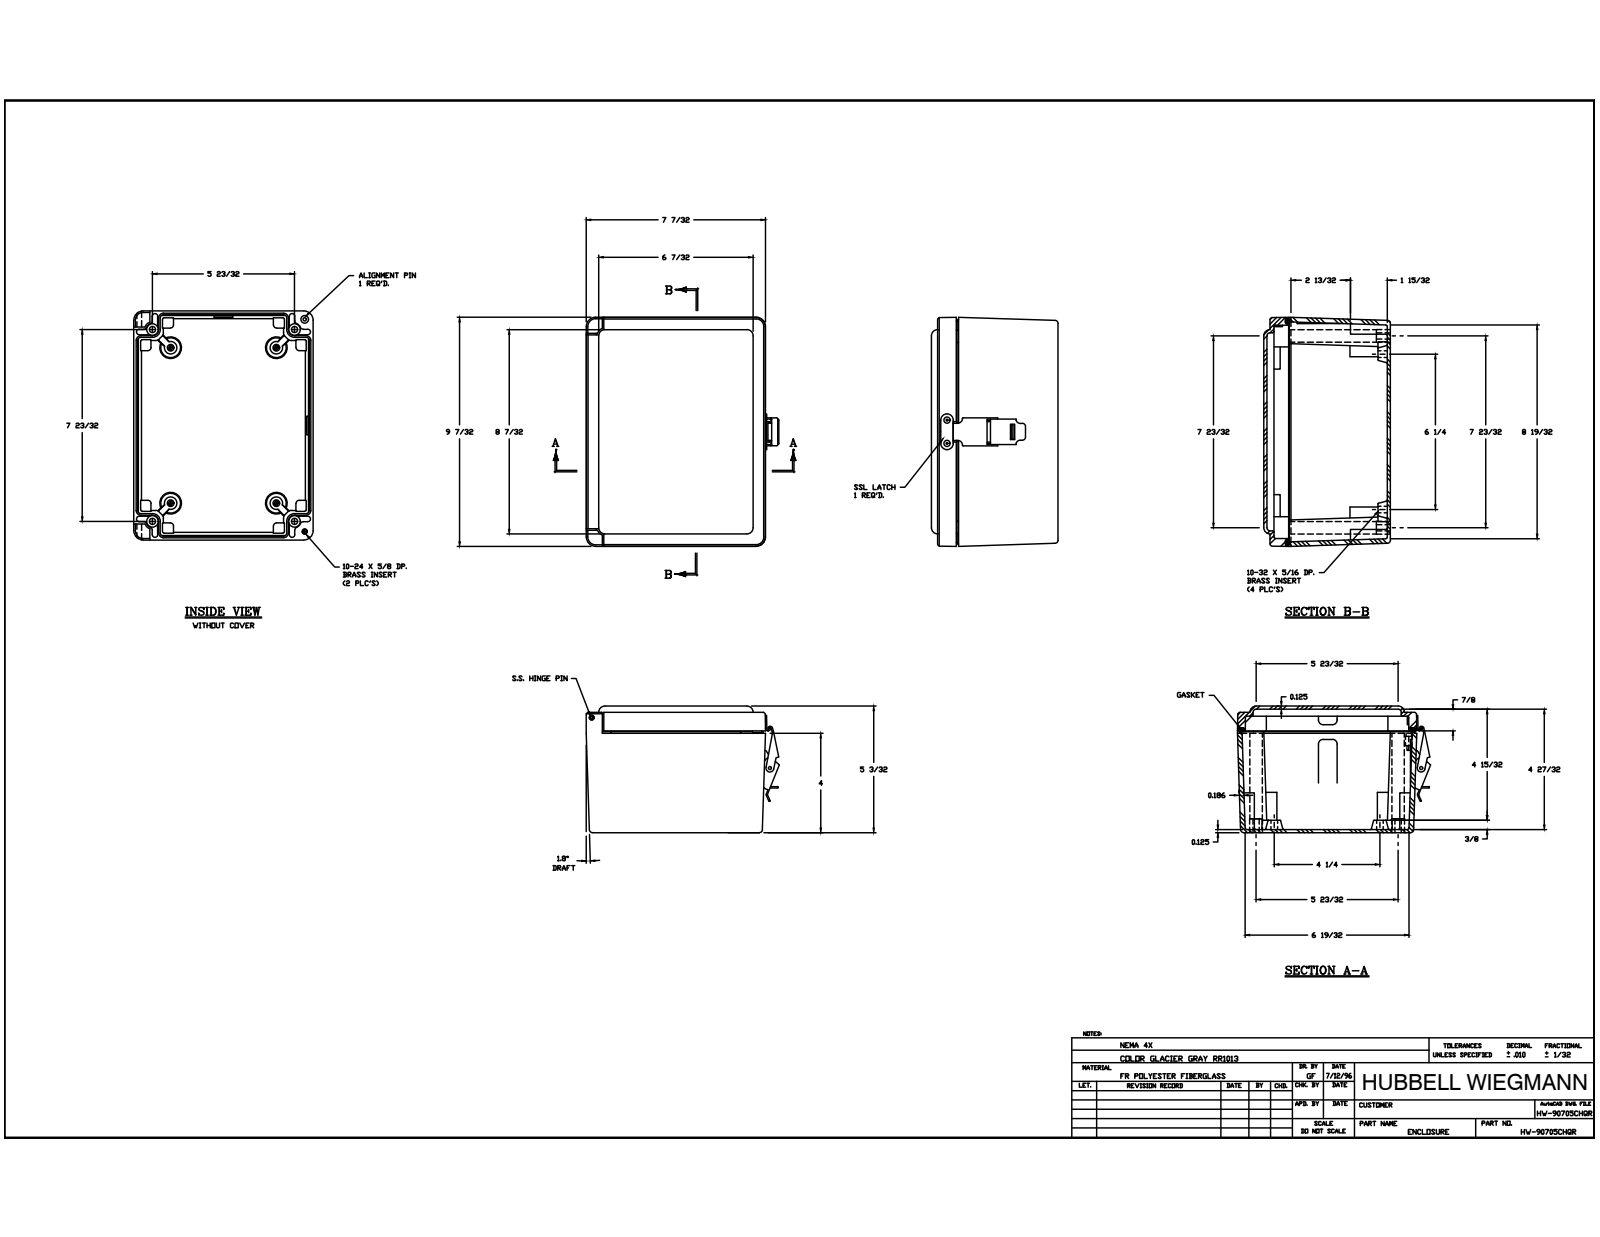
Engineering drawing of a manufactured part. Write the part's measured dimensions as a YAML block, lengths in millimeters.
part_name: "WP907HPLBOX; 0.3125-18 X 0.563 DP BRASS INSERT; 10-32 X0.3125 DP BRASS INSERT; 10-24 X 0.625 DP BRASS INSERT (+8 more)"
step_written_by: "Autodesk Inventor 2014 (AUTOMOTIVE_DESIGN)"
units: millimeters
bodies: {solids: 30, faces: 1114, planar: 435, cylindrical: 379, other: 300}
overall_size: [234.19, 198.58, 129.38]
volume: 942695
surface_area: 429762
round_holes:
  - {diameter: 7.14, count: 6}
  - {diameter: 2.64, count: 4}
  - {diameter: 3.56, count: 4}
  - {diameter: 3.96, count: 4}
  - {diameter: 3.97, count: 4}
  - {diameter: 7.94, count: 4}
  - {diameter: 13.49, count: 4}
  - {diameter: 2.44, count: 2}
  - {diameter: 2.49, count: 2}
  - {diameter: 3.3, count: 2}
  - {diameter: 3.43, count: 2}
  - {diameter: 3.68, count: 2}
round_bosses_or_shafts:
  - {diameter: 9.52, count: 2}
  - {diameter: 9.42, count: 2}
  - {diameter: 5.94, count: 2}
  - {diameter: 4.52, count: 2}
  - {diameter: 2.42, count: 2}
  - {diameter: 2.24, count: 2}
  - {diameter: 7.62, count: 1}
  - {diameter: 7.6, count: 1}
partial_cylinders:
  - {radius: 0.79, count: 60}
  - {radius: 3.17, count: 38}
  - {radius: 1.59, count: 29}
  - {radius: 6.35, count: 10}
  - {radius: 1.14, count: 8}
  - {radius: 1.5, count: 8}
  - {radius: 4.78, count: 8}
  - {radius: 9.53, count: 8}
face_to_face_distances: [3.17, 126.21, 4.72, 129.38, 123.04, 3.18, 123.03, 119.86, 6.35, 19.05]
hole_center_spacings: [14.58, 26.39, 40.97, 128.01, 139.98, 155.95, 178.42, 189.97]
